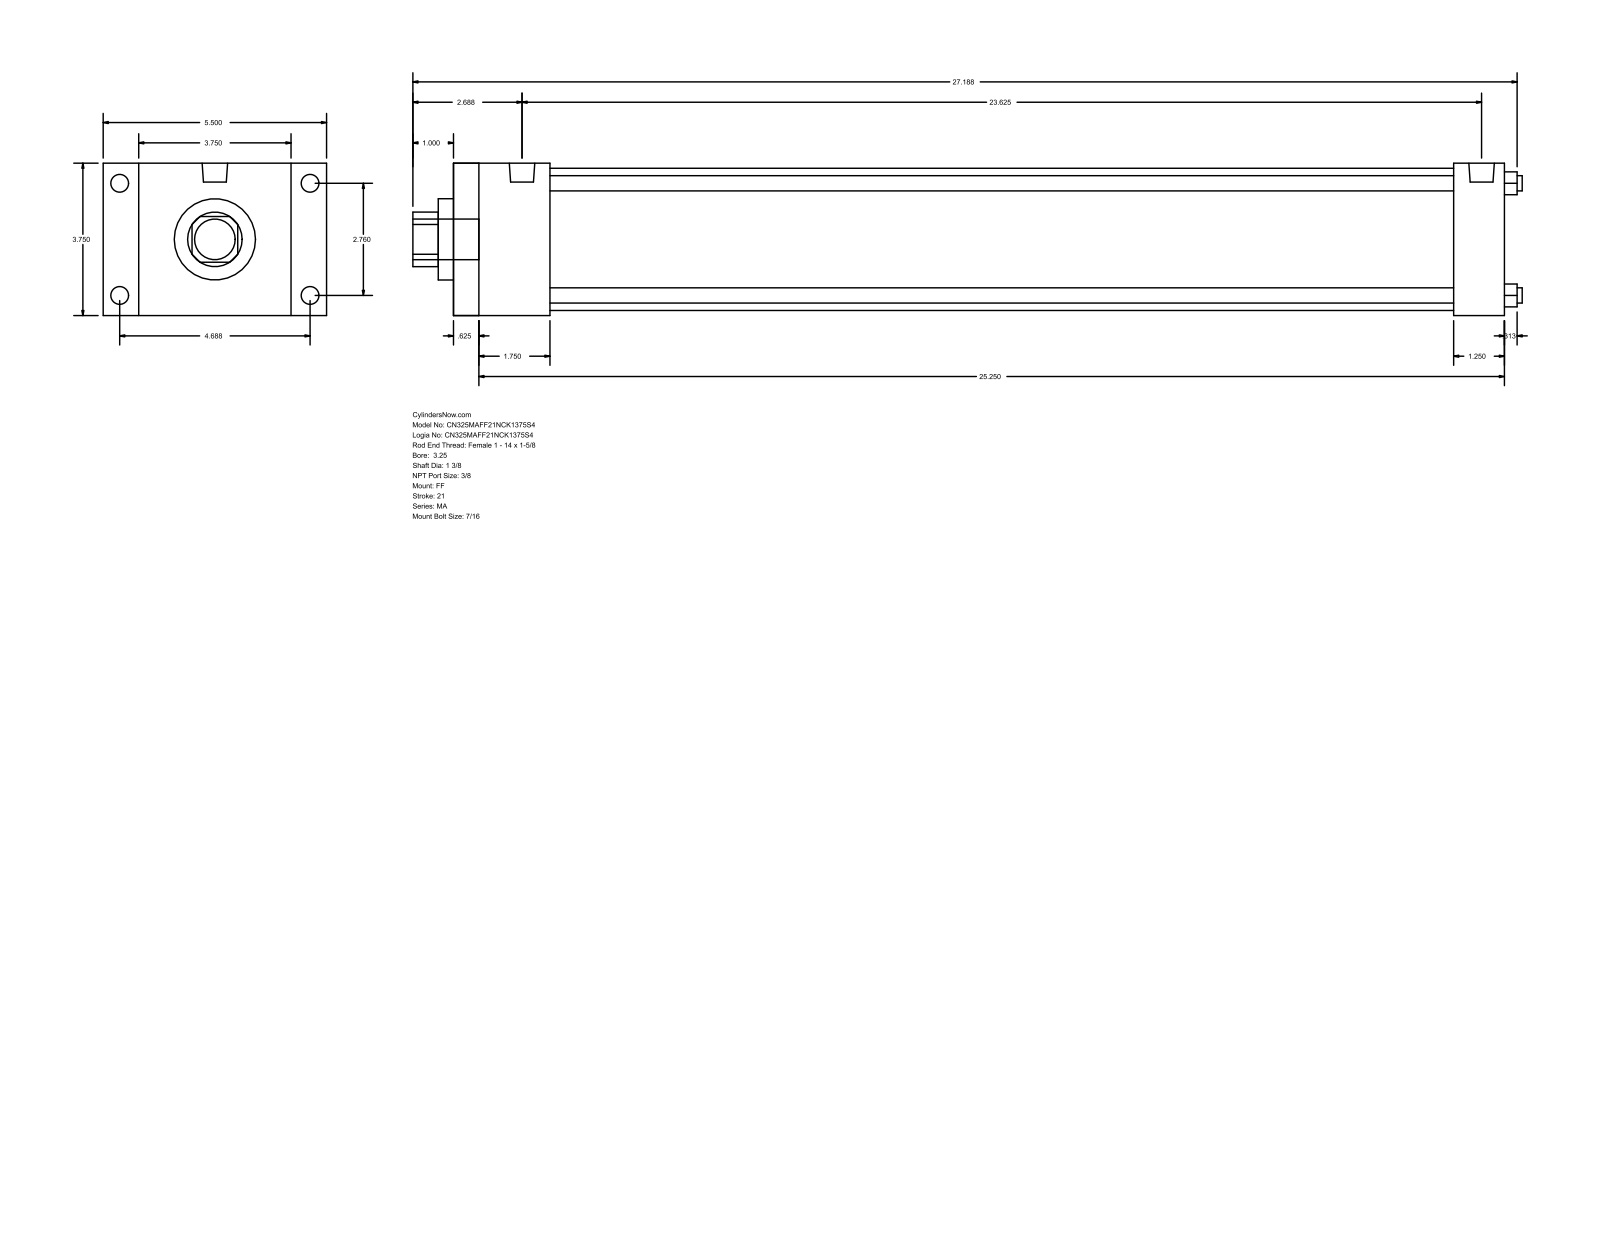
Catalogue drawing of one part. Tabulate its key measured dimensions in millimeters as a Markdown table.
| quantity | value |
| --- | --- |
| part name | MA_FF__0325_1.375 |
| STEP written by | GSSL Pune (CONFIG_CONTROL_DESIGN) |
| units | millimeters |
| bodies | 0 solids, 92 faces (64 planar, 28 cylindrical, 0 other) |
| overall size | 693.74 × 139.7 × 95.25 |
| round holes (diameter × count) | 9.53 × 4, 34.92 × 1, 50.8 × 1, 88.9 × 1 |
| round bosses / shafts (diameter × count) | 11.11 × 8, 15.93 × 2, 25.4 × 1 |
| partial cylindrical surfaces (radius × count) | 17.06 × 1 |
| main face-to-face distances | 95.24, 657.22, 15.87, 641.35, 22.23, 117.47, 60.32, 625.48, 44.45, 609.61 |
| hole center spacings | 49.57, 70.1, 99.14 |
